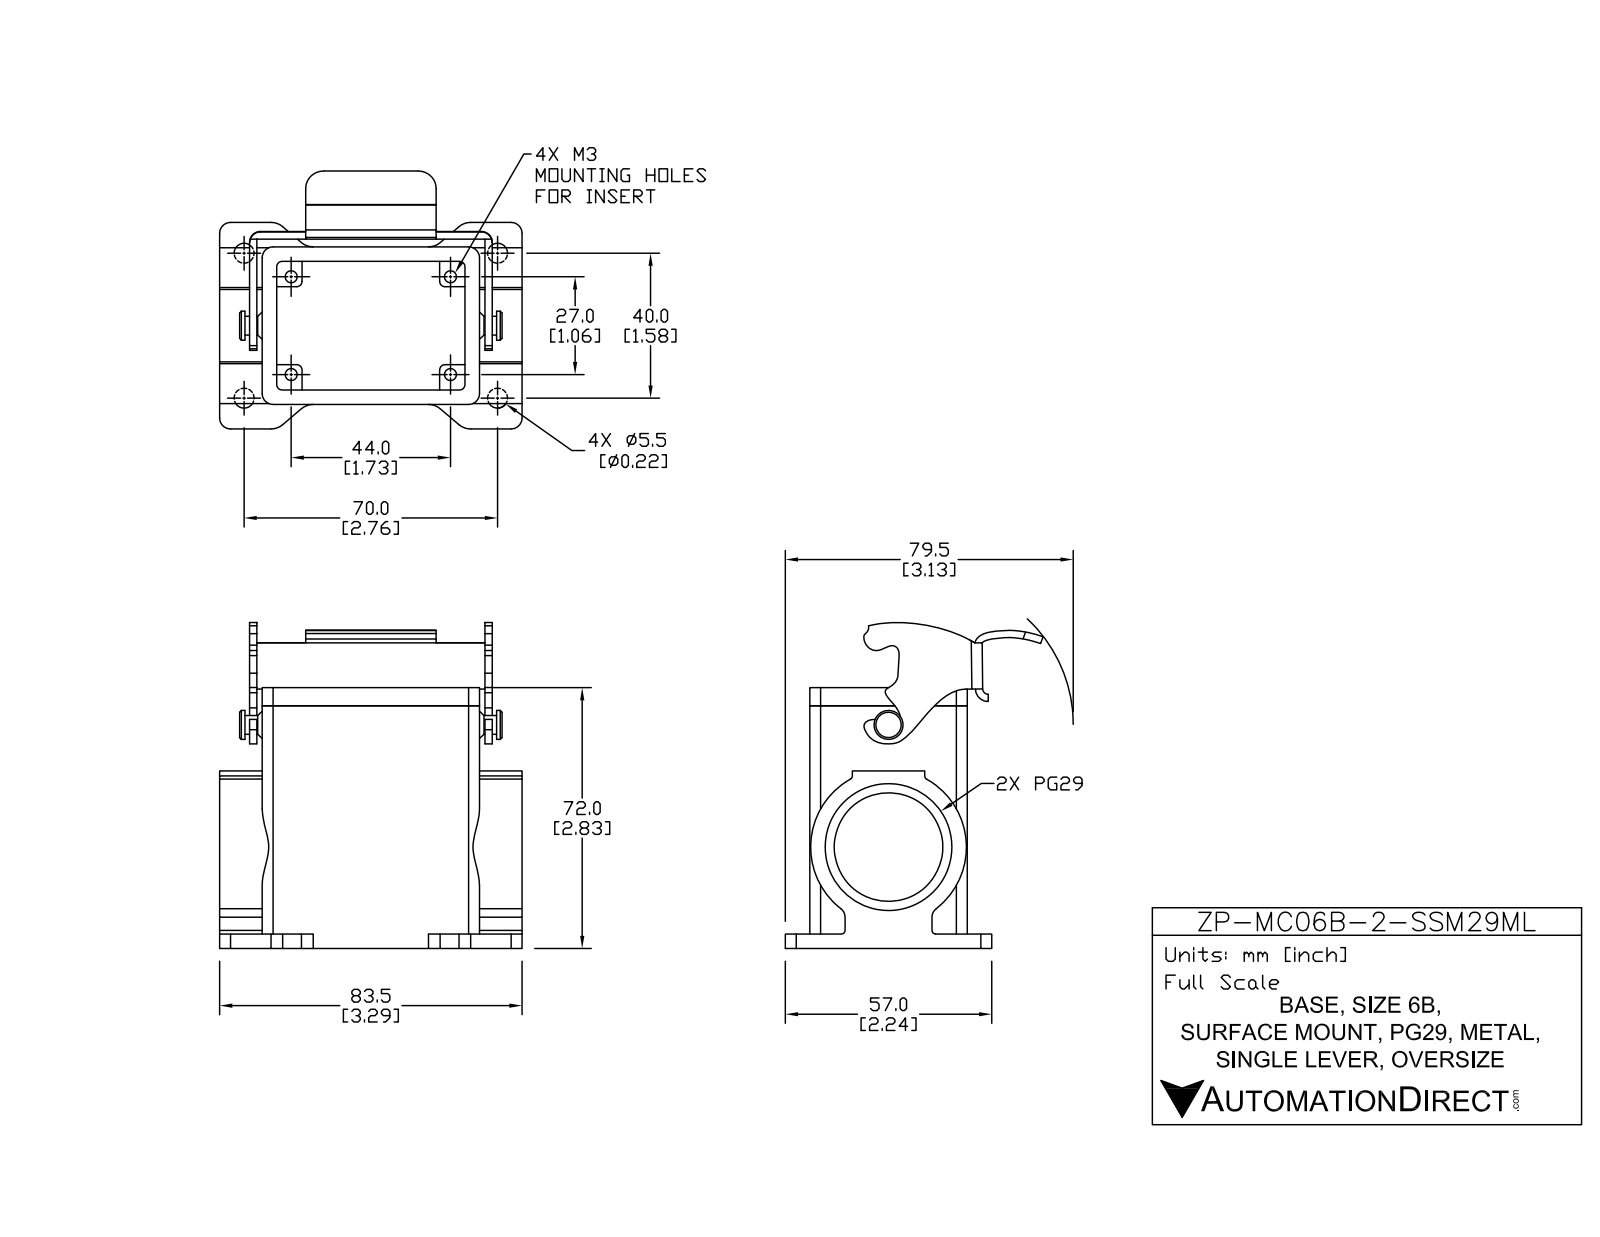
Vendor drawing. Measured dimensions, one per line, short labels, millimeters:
name: ZP-MC06B-2-SSM29ML
written by: SolidWorks 2011 (AUTOMOTIVE_DESIGN)
unit: mm
bodies: 3 solids, 264 faces (110 planar, 144 cylindrical, 10 other)
size: 85.48 × 83.5 × 75.98
volume: 87 541 mm³; area: 48 100 mm²
holes: 4× ⌀3.5, 4× ⌀5.5, 1× ⌀30, 1× ⌀35
bosses: 1× ⌀8, 1× ⌀5.17
rounds: 13× R0.5, 11× R3, 9× R5, 8× R1.5, 4× R1, 3× R4, 2× R0.25, 2× R10
face distances: 4, 39.5, 43.5, 35.5, 56, 7, 1.15, 11, 11.75, 15.75
hole spacings: 15.21, 35.65, 56.93, 65.43, 26, 40, 43, 50.25
